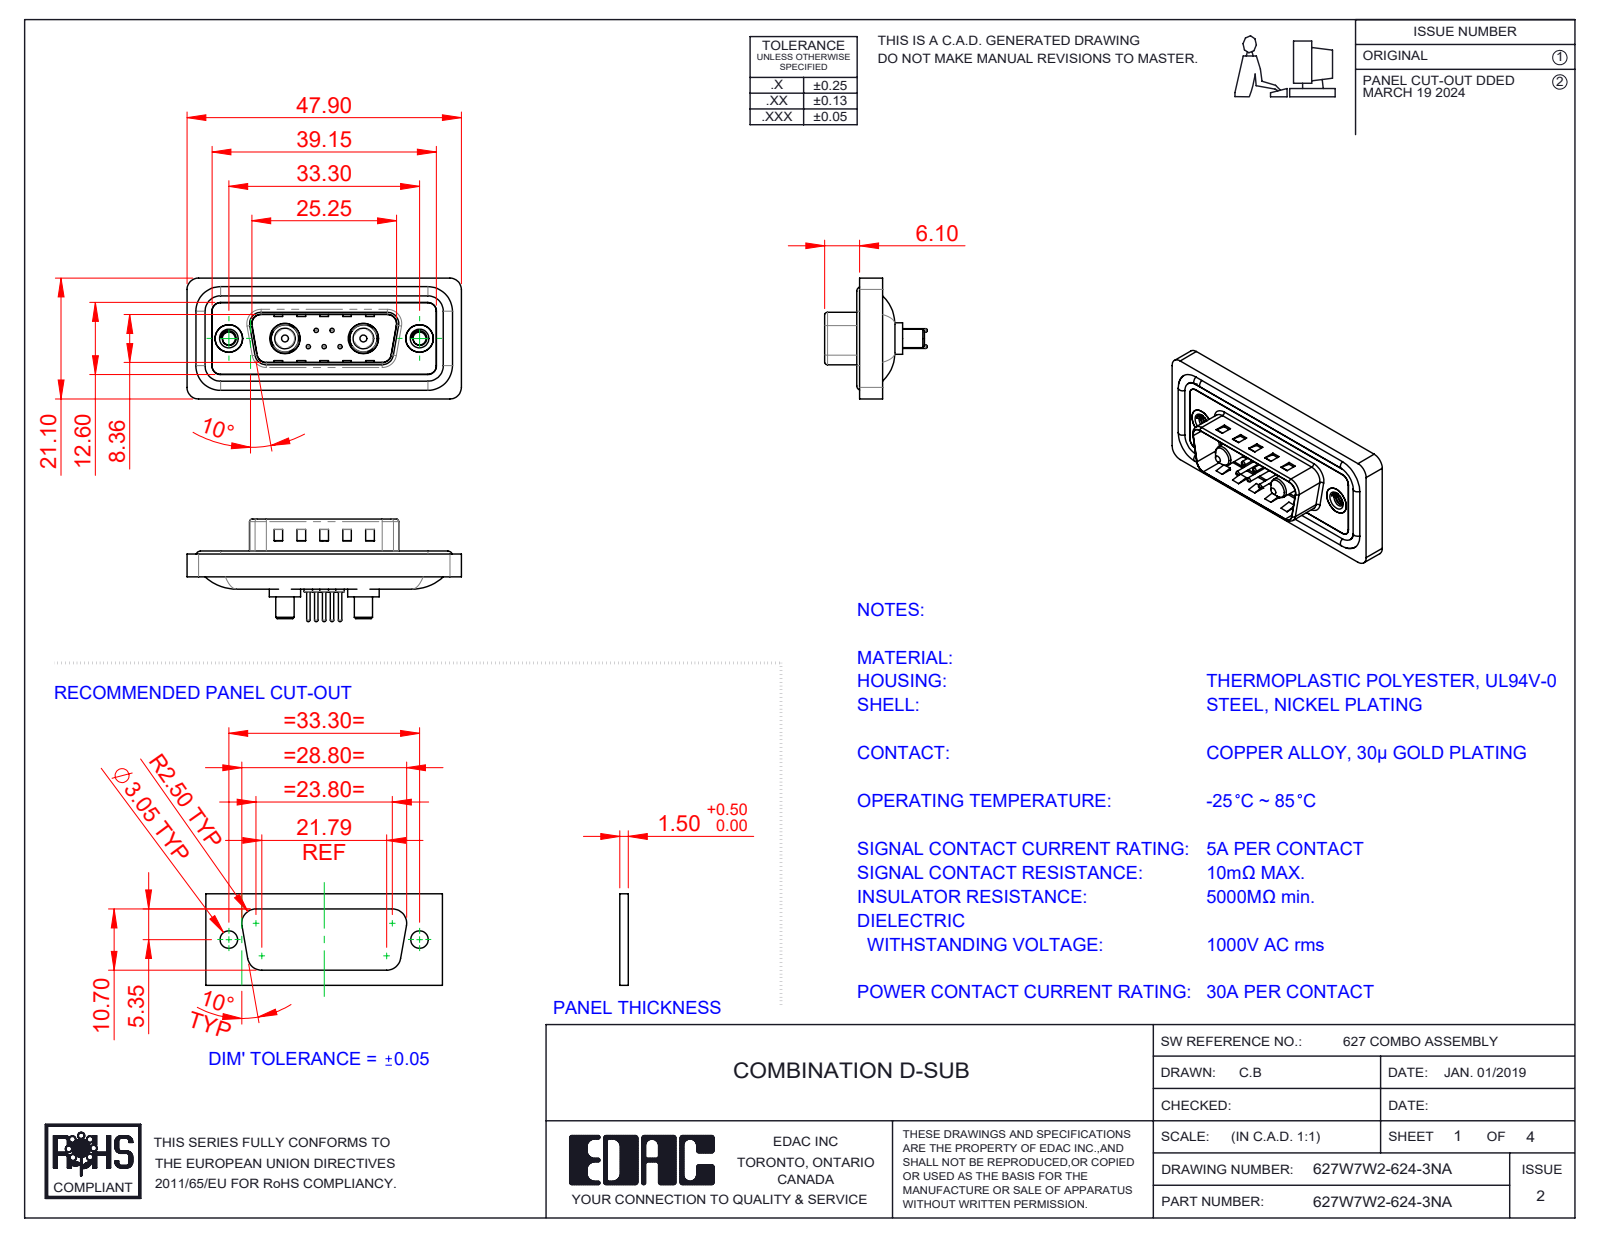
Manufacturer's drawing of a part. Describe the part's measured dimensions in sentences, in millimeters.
The part is named "627Combo Shell Front_15 Contacts; 627Combo Contact Row 2_24; Power Pin_30A S; 627Combo Threaded Rivet_A (+5 more)". Its 3-D file was written by "SolidWorks 2023 (CONFIG_CONTROL_DESIGN)". It is 16 solids with 708 faces: 232 planar, 294 cylindrical and 182 other. Overall it measures 47.9 by 21.1 by 17.9 millimeters. Its volume is 5 533 cubic millimeters and its surface area 8 800 square millimeters. Round holes: 5 of diameter 0.75, 5 of diameter 1.6, 5 of diameter 2, 2 of diameter 2.26, 2 of diameter 4, 2 of diameter 4.8, 2 of diameter 4.85, 2 of diameter 5, 2 of diameter 5.3. Round bosses or shafts: 5 of diameter 1.5, 5 of diameter 0.6, 4 of diameter 1.6, 2 of diameter 5.5, 2 of diameter 5.2, 2 of diameter 4.9, 2 of diameter 4.75, 2 of diameter 3.75. Partial cylindrical surfaces (rounded edges, fillets, slot ends): 26 of radius 1.5, 20 of radius 2, 8 of radius 0.5, 8 of radius 1.6, 4 of radius 0.25, 4 of radius 0.6, 4 of radius 0.65, 4 of radius 0.9. The main face-to-face distances are 0.4, 1.1, 1.5, 1.6, 0.5, 3.1, 2.9, 0.82, 9.58, 2.5. The hole center spacings are 3.16, 2.77, 9.8, 23.5, 4.31, 4.33, 5.03, 5.04.
